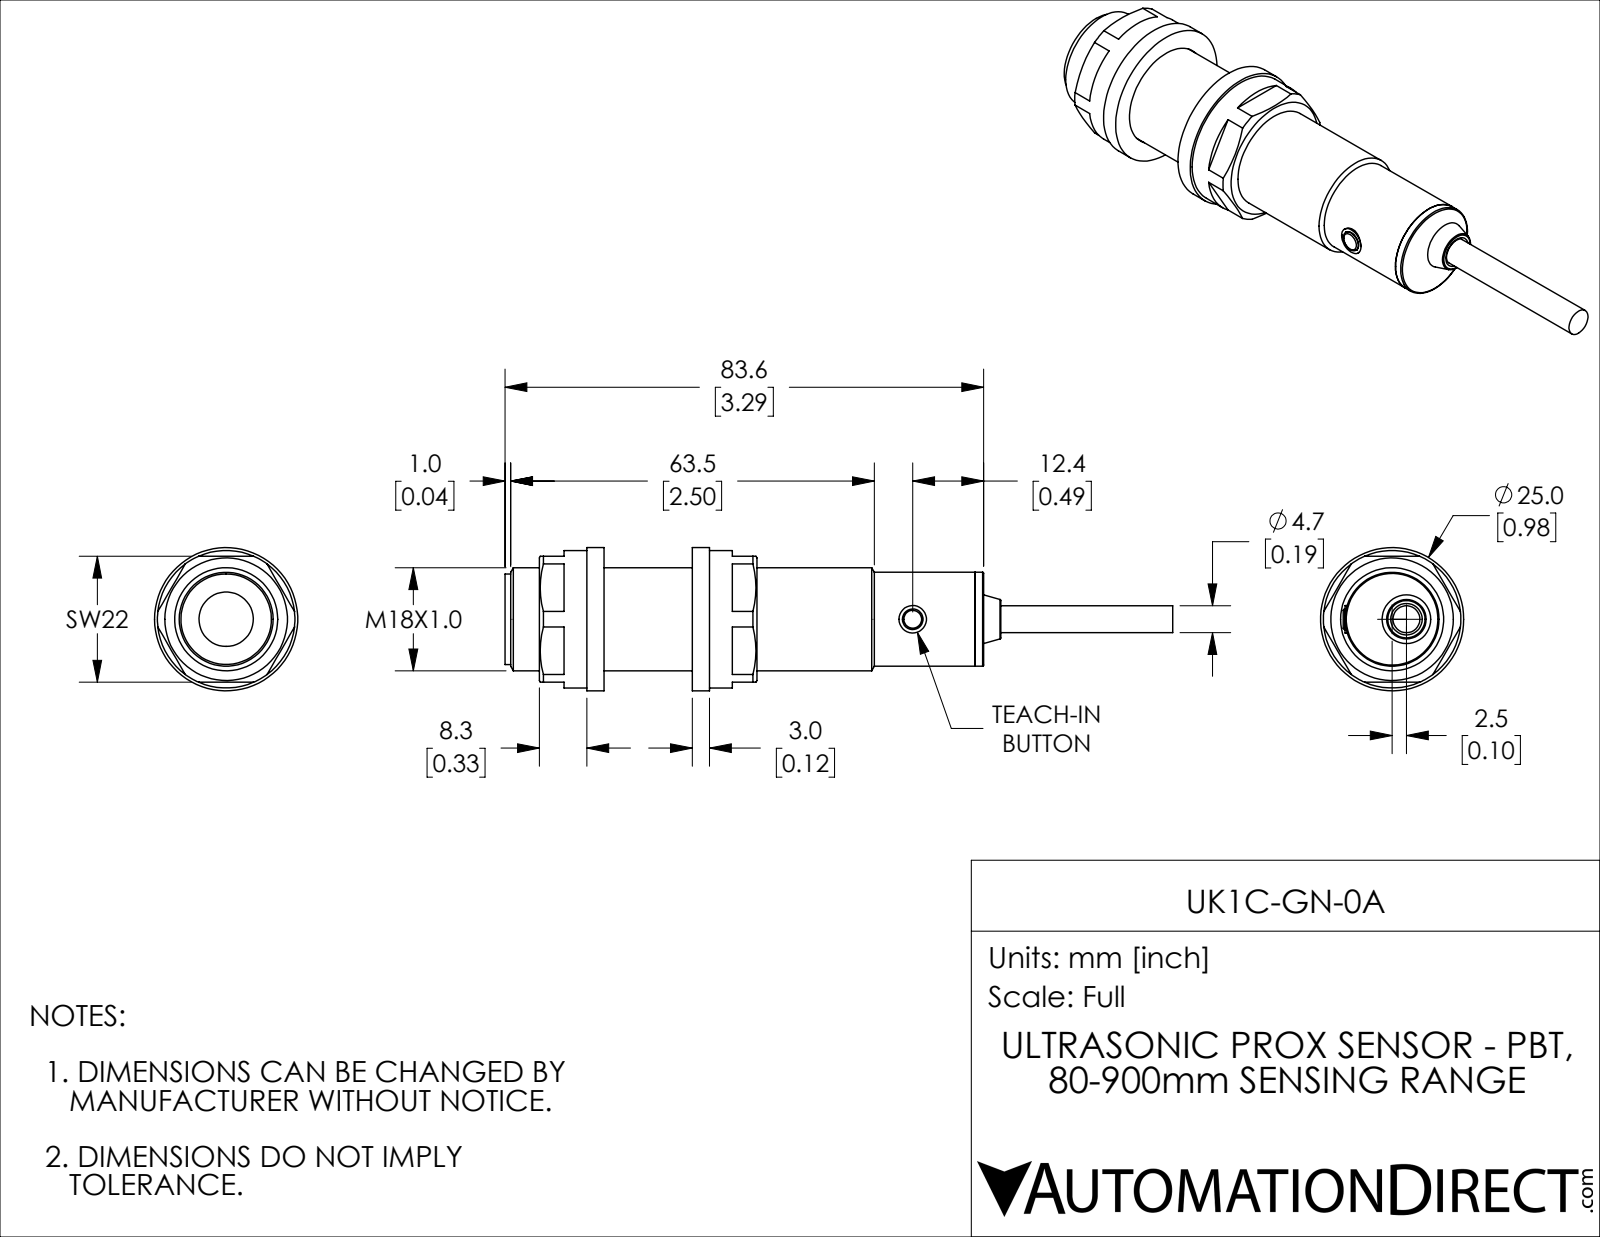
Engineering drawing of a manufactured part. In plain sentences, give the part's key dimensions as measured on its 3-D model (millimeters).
The part is named "UK1C-GN-0A". Its 3-D file was written by "SolidWorks 2018 (AUTOMOTIVE_DESIGN)". It is 10 solids with 107 faces: 49 planar, 40 cylindrical and 18 other. Overall it measures 116.6 by 25 by 25 millimeters. Its volume is 25 220 cubic millimeters and its surface area 11 419 square millimeters. Round holes: 2 of diameter 4.7, 1 of diameter 3.6, 1 of diameter 9.5, 1 of diameter 18, 1 of diameter 18.2. Round bosses or shafts: 1 of diameter 25, 1 of diameter 24, 1 of diameter 16.4, 1 of diameter 15.8, 1 of diameter 5.4, 1 of diameter 4.8. The main face-to-face distances are 3, 18.4, 21.4, 67.8, 46.4, 13.3, 34.7, 81.1, 16.3, 64.8. The hole center spacings are 2.5.
